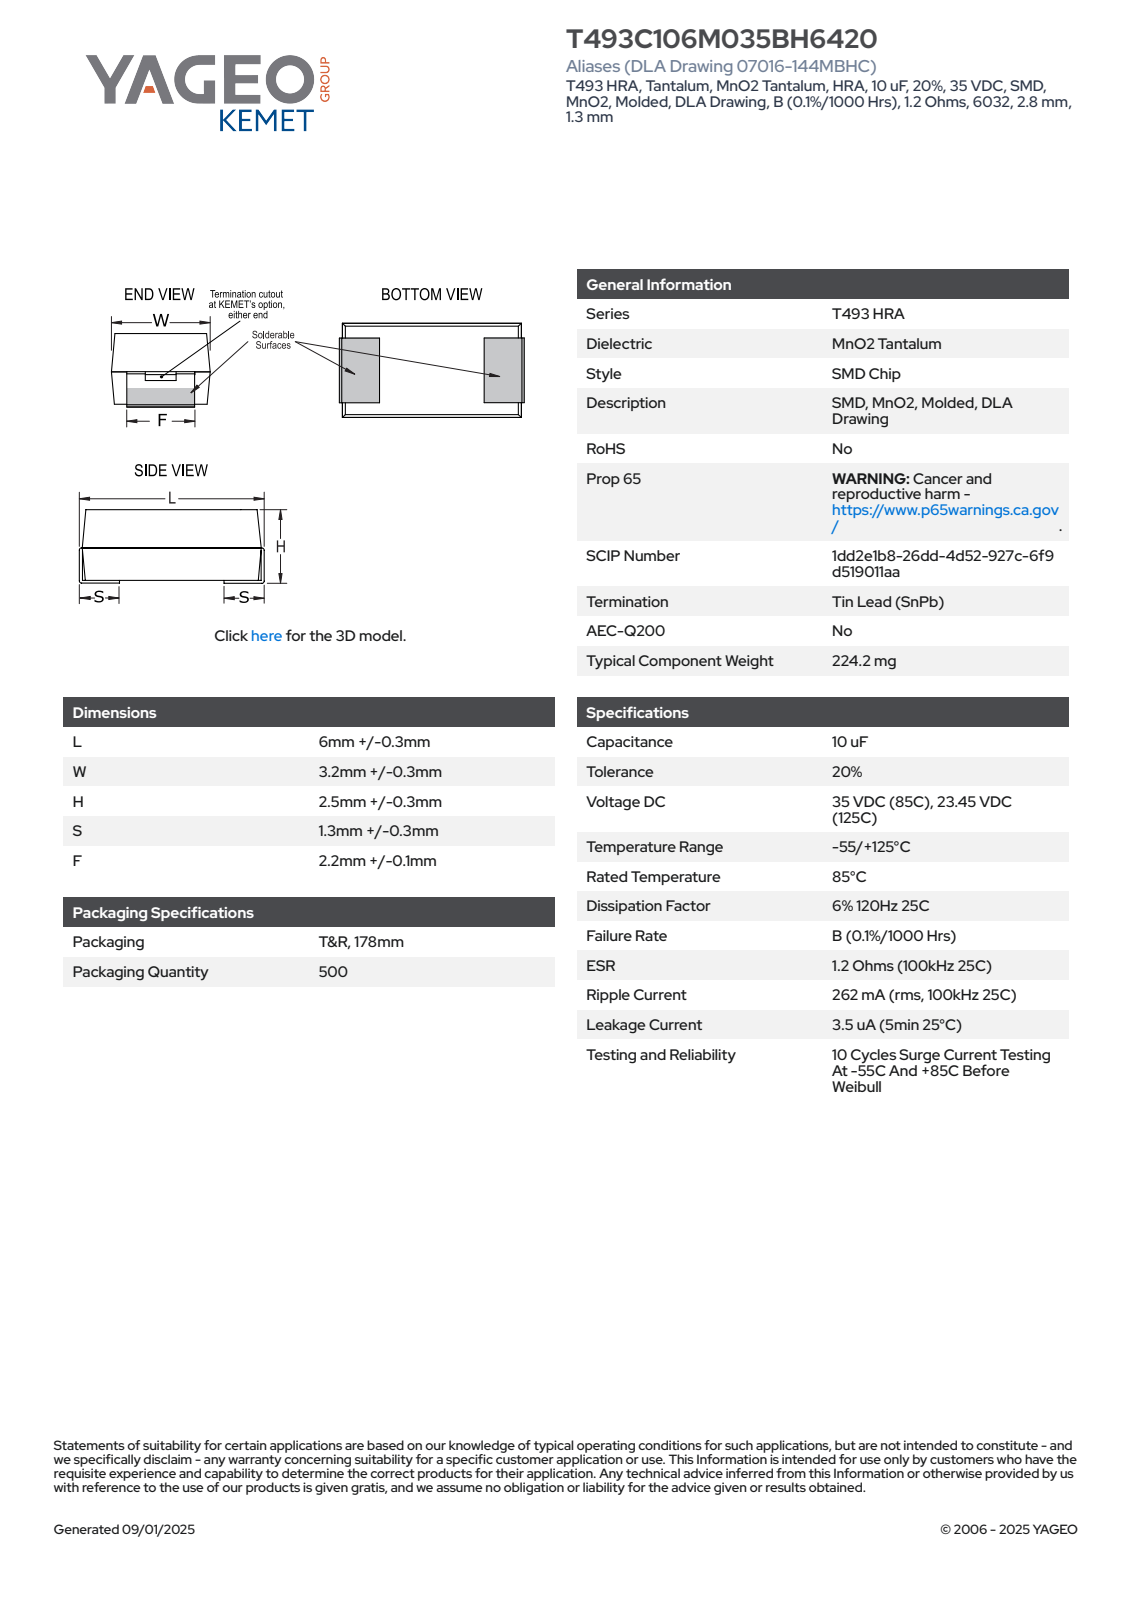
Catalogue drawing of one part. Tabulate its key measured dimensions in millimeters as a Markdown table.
| quantity | value |
| --- | --- |
| part name | CTSM_Case_Top_23; CTSM_Case_Anode_23; CTSM_Case_Cathode_23; CTSM_6032_L6.30W3.5H2.80S1.3F2.2 (+1 more) |
| STEP written by | SolidWorks 2014 (AUTOMOTIVE_DESIGN) |
| units | millimeters |
| bodies | 7 solids, 94 faces (90 planar, 4 cylindrical, 0 other) |
| overall size | 6.3 × 3.5 × 2.8 |
| volume | 55 mm³ |
| surface area | 156 mm² |
| main face-to-face distances | 1.25, 1.42, 2.67, 3.48, 6.02, 6.17, 1.38, 2.8, 2.77, 1.35 |
